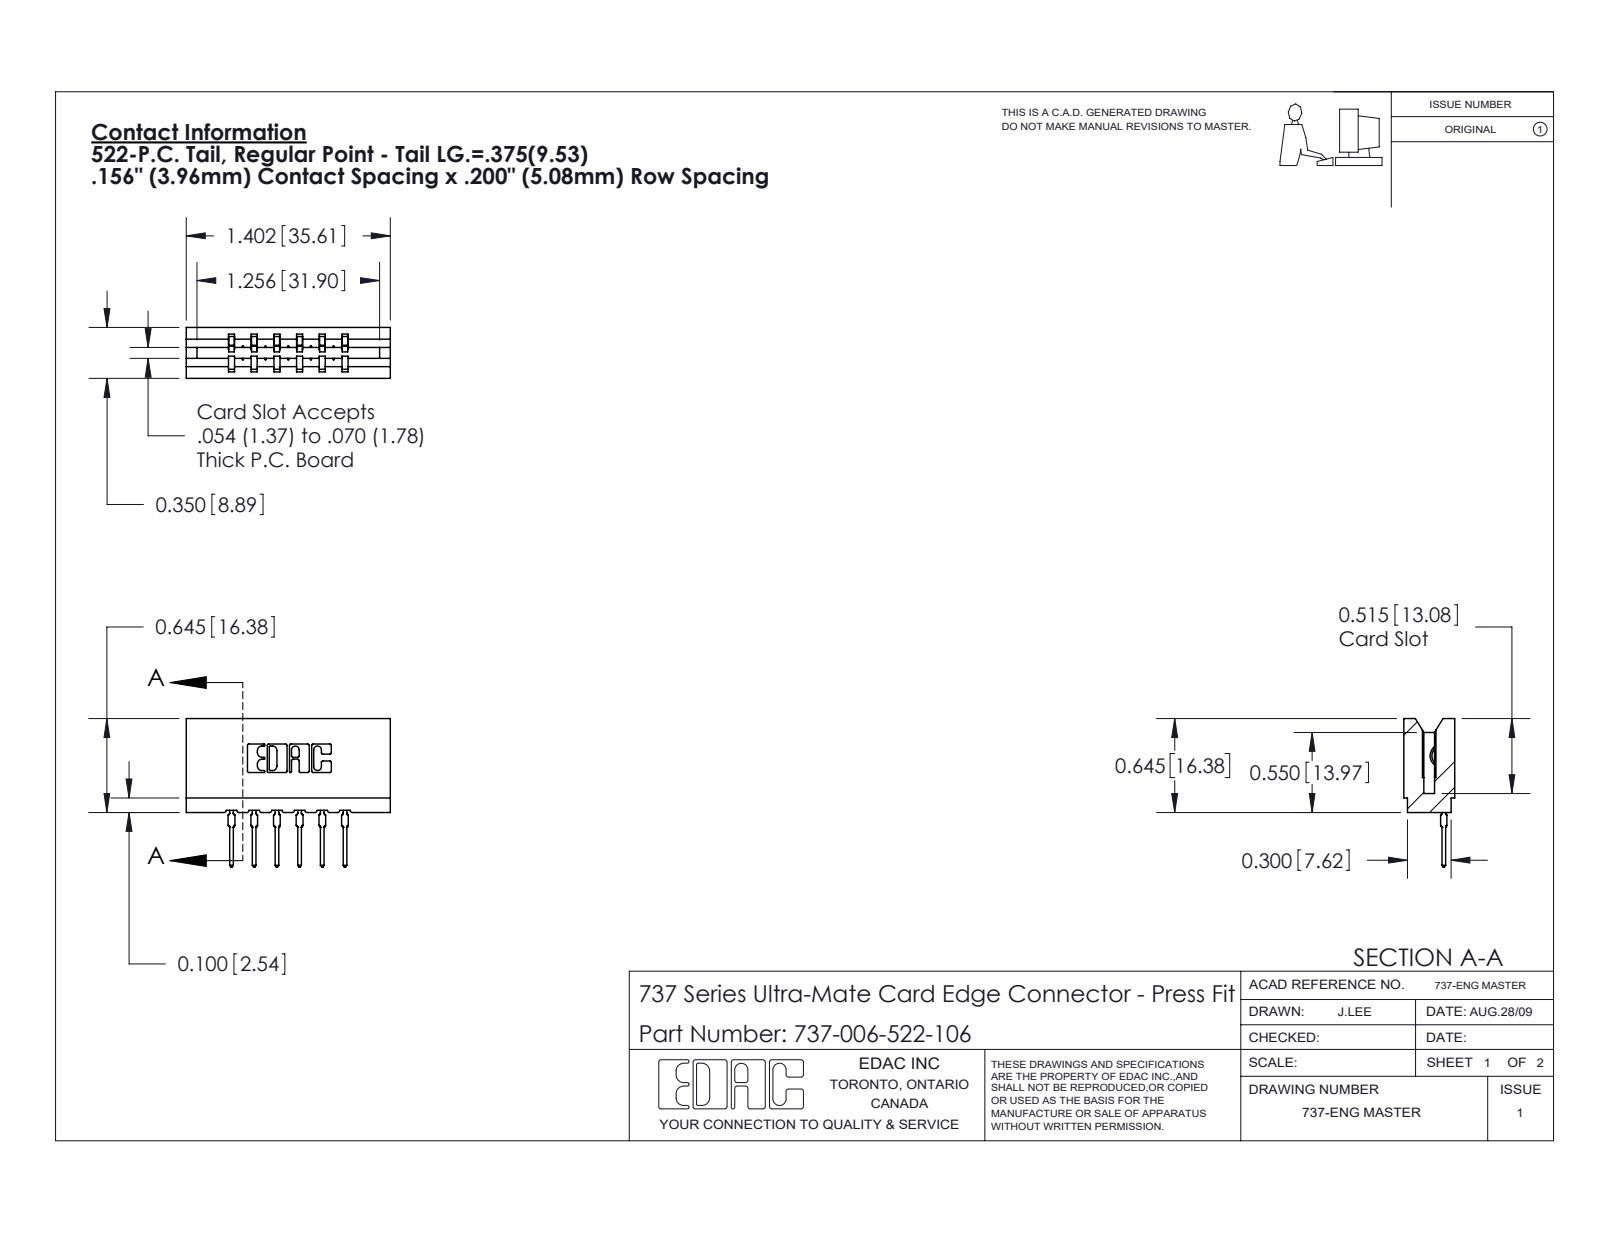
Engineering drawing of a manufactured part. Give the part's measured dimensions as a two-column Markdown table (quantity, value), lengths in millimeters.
| quantity | value |
| --- | --- |
| part name | 737 Part_Insulator Option - 06; 745-292-001_522; 737-006-522-106 |
| STEP written by | SolidWorks 2020 (CONFIG_CONTROL_DESIGN) |
| units | millimeters |
| bodies | 7 solids, 773 faces (463 planar, 154 cylindrical, 156 other) |
| overall size | 35.6 × 25.9 × 8.9 |
| volume | 3 670 mm³ |
| surface area | 4 295 mm² |
| partial cylindrical surfaces (radius × count) | 0.3 × 22, 0.4 × 12, 0.5 × 12, 0.2 × 6, 0.8 × 6, 0.1 × 4, 0.3 × 4, 0.7 × 3 |
| main face-to-face distances | 4, 3.5, 5.4, 8.9, 7.9, 9, 5, 1.9, 11.9, 13 |
